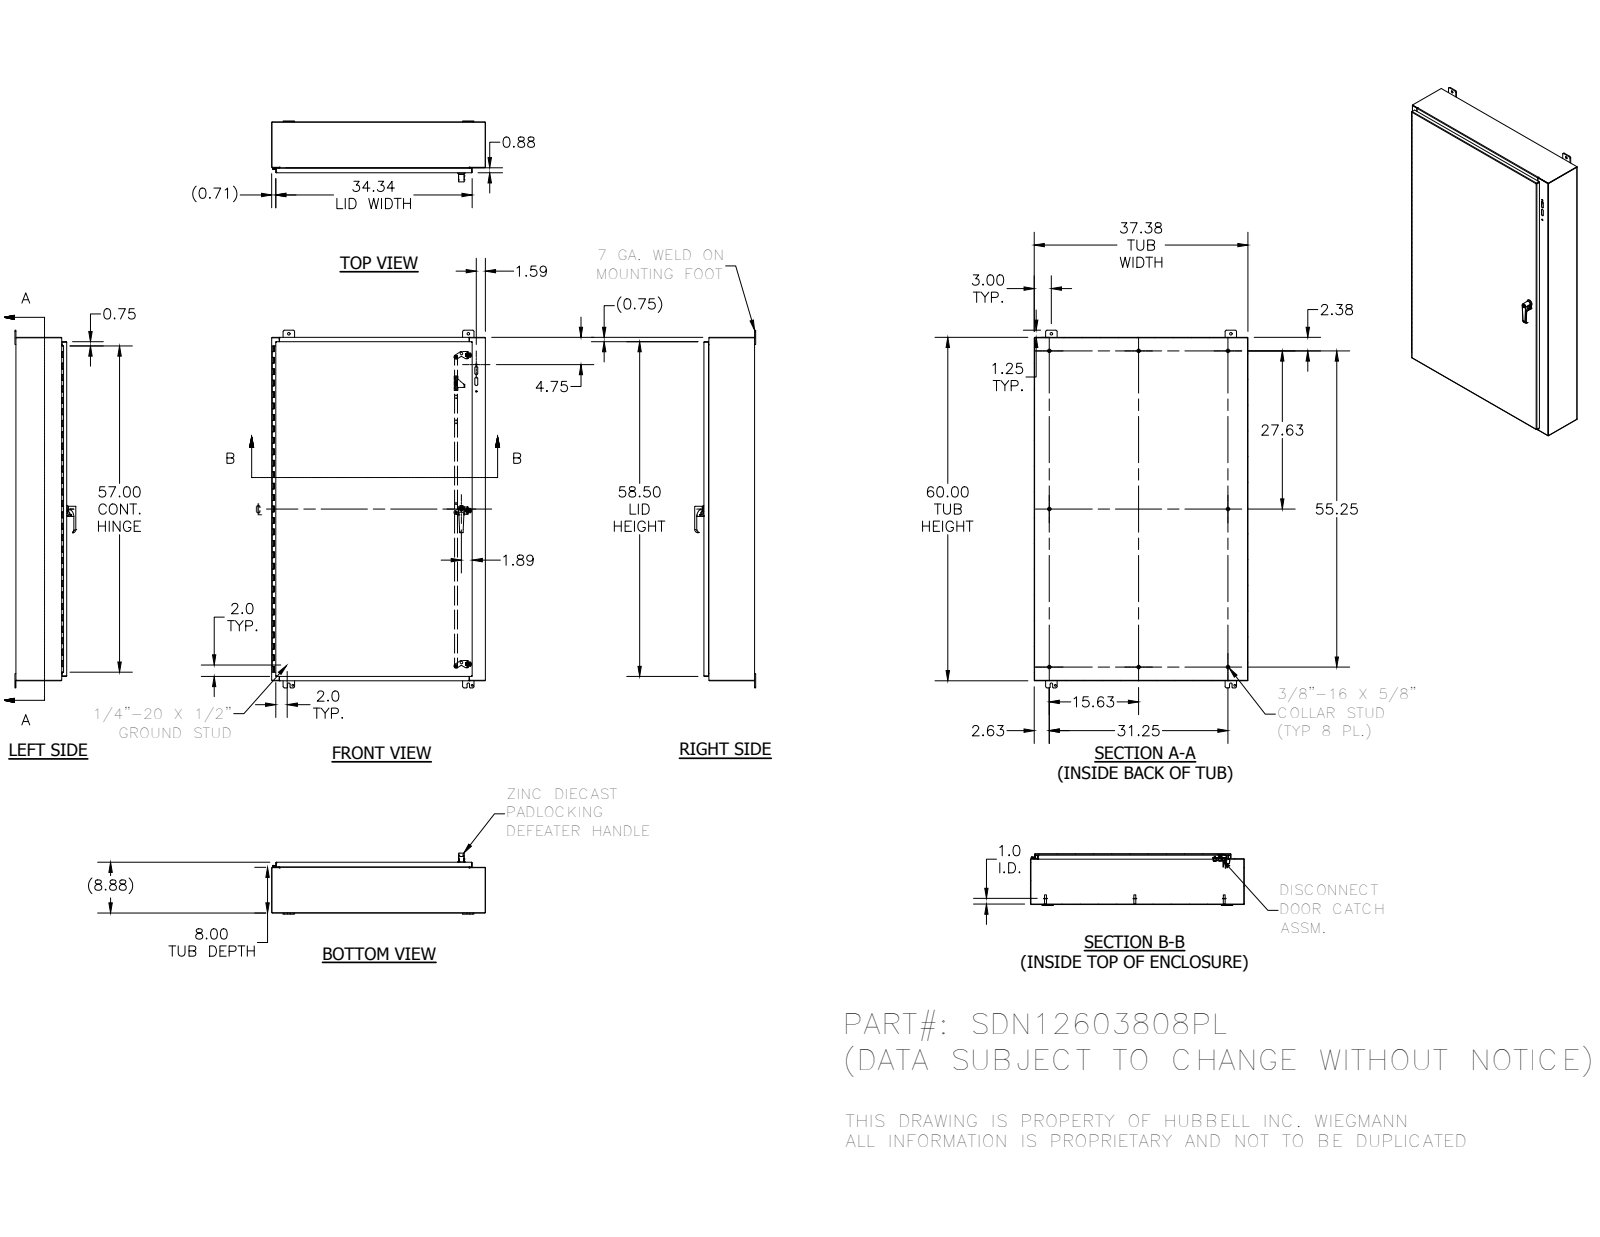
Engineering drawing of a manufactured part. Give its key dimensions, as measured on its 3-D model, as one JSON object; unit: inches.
{"part_name": "SDN12603808PL; SDN12603808PLBLR; 3889; 34840 (+8 more)", "step_written_by": "Autodesk Inventor 2012 (AUTOMOTIVE_DESIGN)", "units": "inches", "bodies": {"solids": 64, "faces": 1997, "planar": 1084, "cylindrical": 659, "other": 254}, "overall_size": [62.5, 37.375, 10.649], "volume_in3": 495.8, "surface_area_in2": 13311, "round_holes": [[0.145, 6], [0.313, 4], [0.32, 4], [0.438, 4], [0.196, 3], [0.211, 3], [0.22, 3], [0.313, 3], [0.45, 3], [0.156, 2], [0.281, 2], [0.307, 2]], "round_bosses_or_shafts": [[0.33, 11], [0.625, 10], [0.437, 6], [0.3, 6], [0.225, 6], [0.25, 4], [0.19, 4], [0.75, 3]], "partial_cylinders_radius": [[0.02, 38], [0.012, 30], [0.025, 24], [0.25, 23], [0.031, 18], [0.105, 18], [0.125, 18], [0.094, 6]], "face_to_face_distances": [0.074, 8.801, 8.727, 8.875, 37.301, 7.926, 0.875, 59.926, 37.227, 37.375], "hole_center_spacings": [26.844, 27.156, 54, 1.593, 31.375, 60, 67.708, 0.5]}
